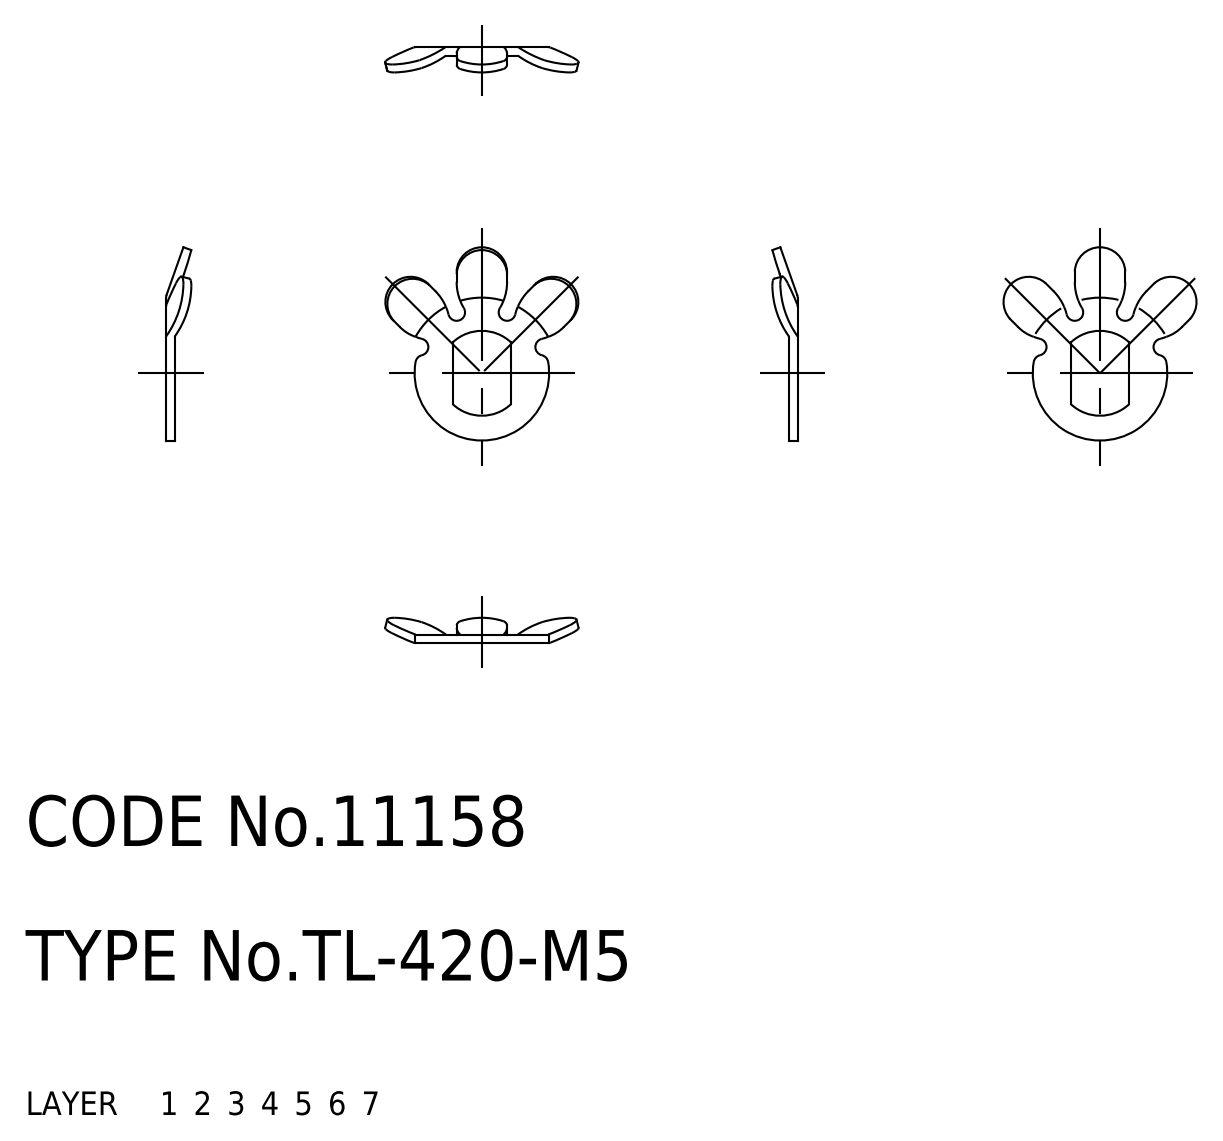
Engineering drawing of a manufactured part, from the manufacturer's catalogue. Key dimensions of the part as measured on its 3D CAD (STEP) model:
Part name (STEP PRODUCT): washer; TL_420_M5
STEP written by: SolidWorks 2015 (AUTOMOTIVE_DESIGN)
Units: millimetres
Bodies: 1 solid, 45 faces (10 planar, 26 cylindrical, 9 other)
Overall size (bounding box): 11.5 × 11.49 × 1.5
Volume: 31 mm³ · Surface area: 154 mm²
Partial cylindrical surfaces — rounded edges, fillets, slot ends (radius × count): R0.5 ×6, R3 ×6, R1.5 ×3, R2.52 ×1, R4 ×1
Main face-to-face distances: 0.5, 3.46, 3, 3.23
